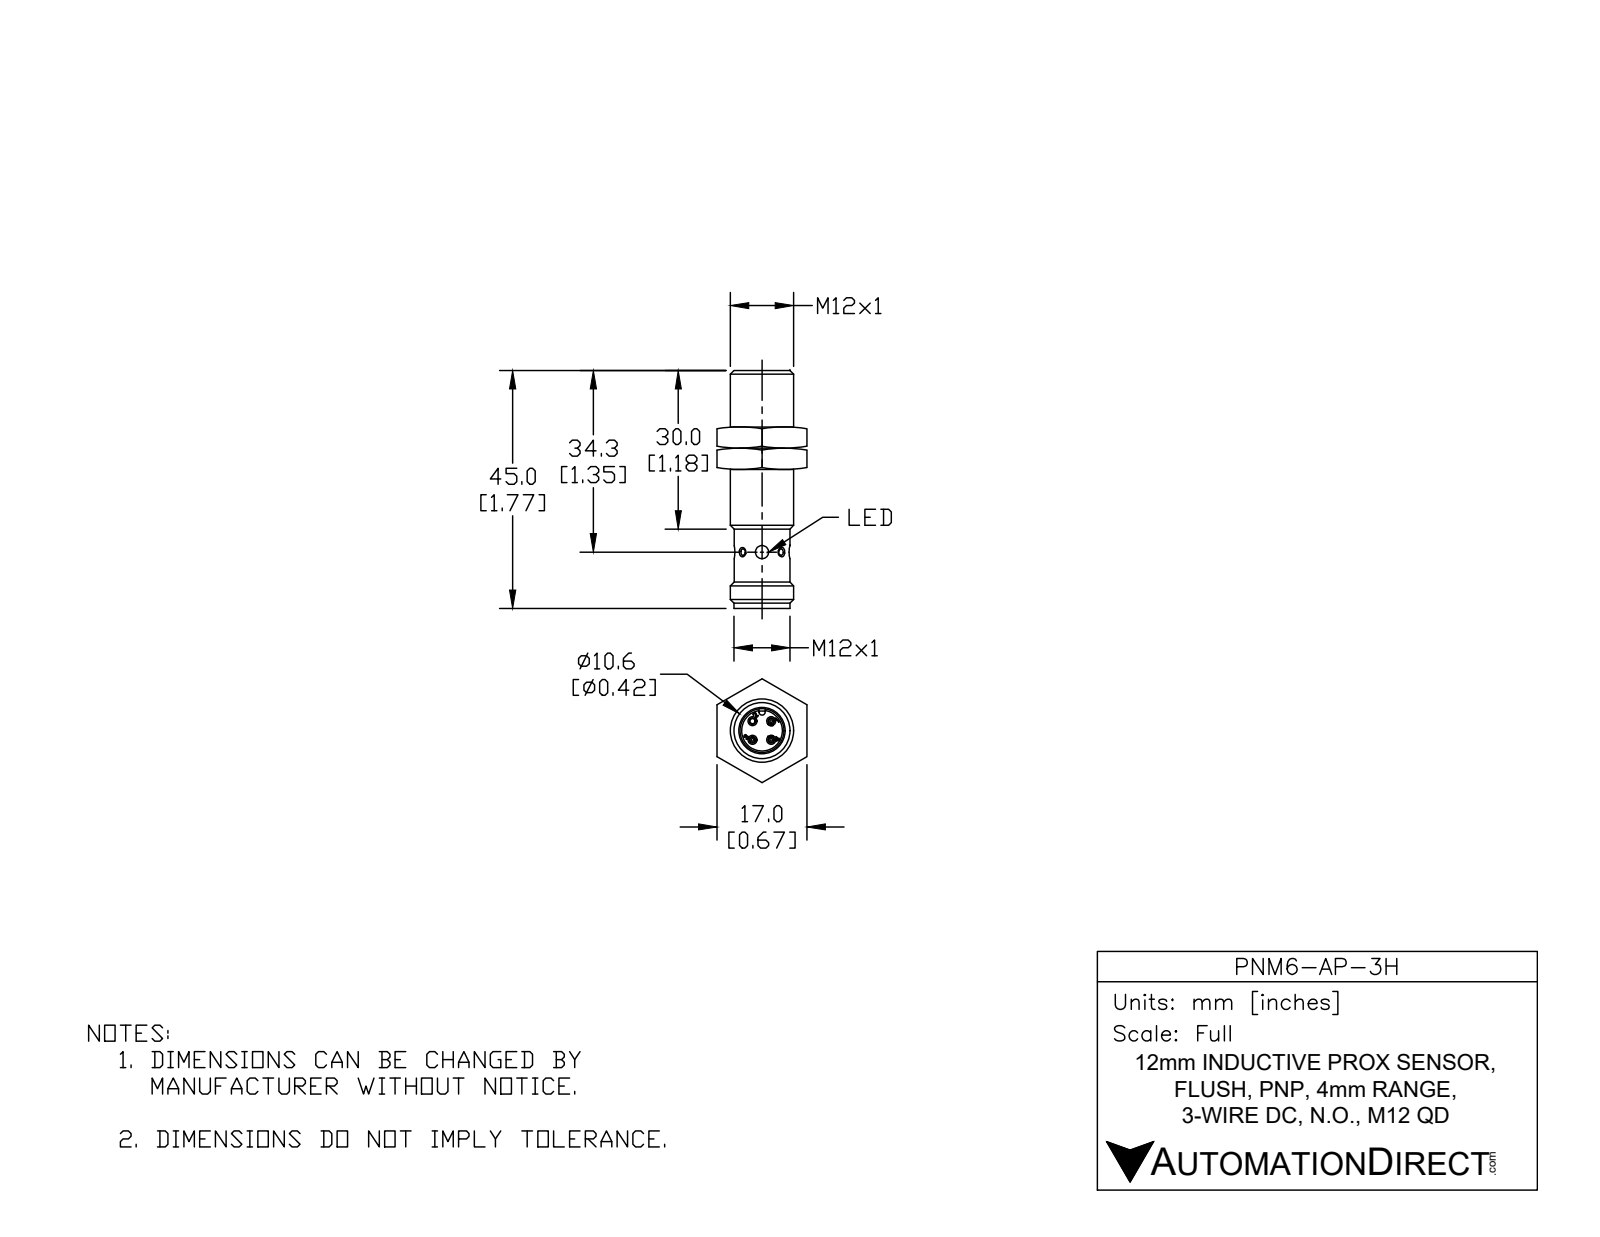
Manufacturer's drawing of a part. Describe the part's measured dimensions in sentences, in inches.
The part is named "PNM6-AP-3H". Its 3-D file was written by "SolidWorks 2017 (AUTOMOTIVE_DESIGN)". It is 1 solid with 491 faces: 117 planar, 138 cylindrical and 236 other. Overall it measures 1.772 by 0.472 by 0.472 inches. Its volume is 0.247 cubic inches and its surface area 8.016 square inches. Round holes: 3 of diameter 0.043, 2 of diameter 0.04, 2 of diameter 0.098, 1 of diameter 0.038, 1 of diameter 0.04, 1 of diameter 0.327, 1 of diameter 0.394, 1 of diameter 0.401. Round bosses or shafts: 6 of diameter 0.039, 1 of diameter 0.472, 1 of diameter 0.417, 1 of diameter 0.415, 1 of diameter 0.4, 1 of diameter 0.392, 1 of diameter 0.39, 1 of diameter 0.38. Partial cylindrical surfaces (rounded edges, fillets, slot ends): 36 of radius 0.004, 6 of radius 0.079, 1 of radius 0.024, 1 of radius 0.031, 1 of radius 0.161. The main face-to-face distances are 0.118, 1.299, 1.181, 0.018, 0.1, 1.281, 1.303, 1.421, 1.404, 0.122. The hole center spacings are 0.098, 0.139, 0.197.
